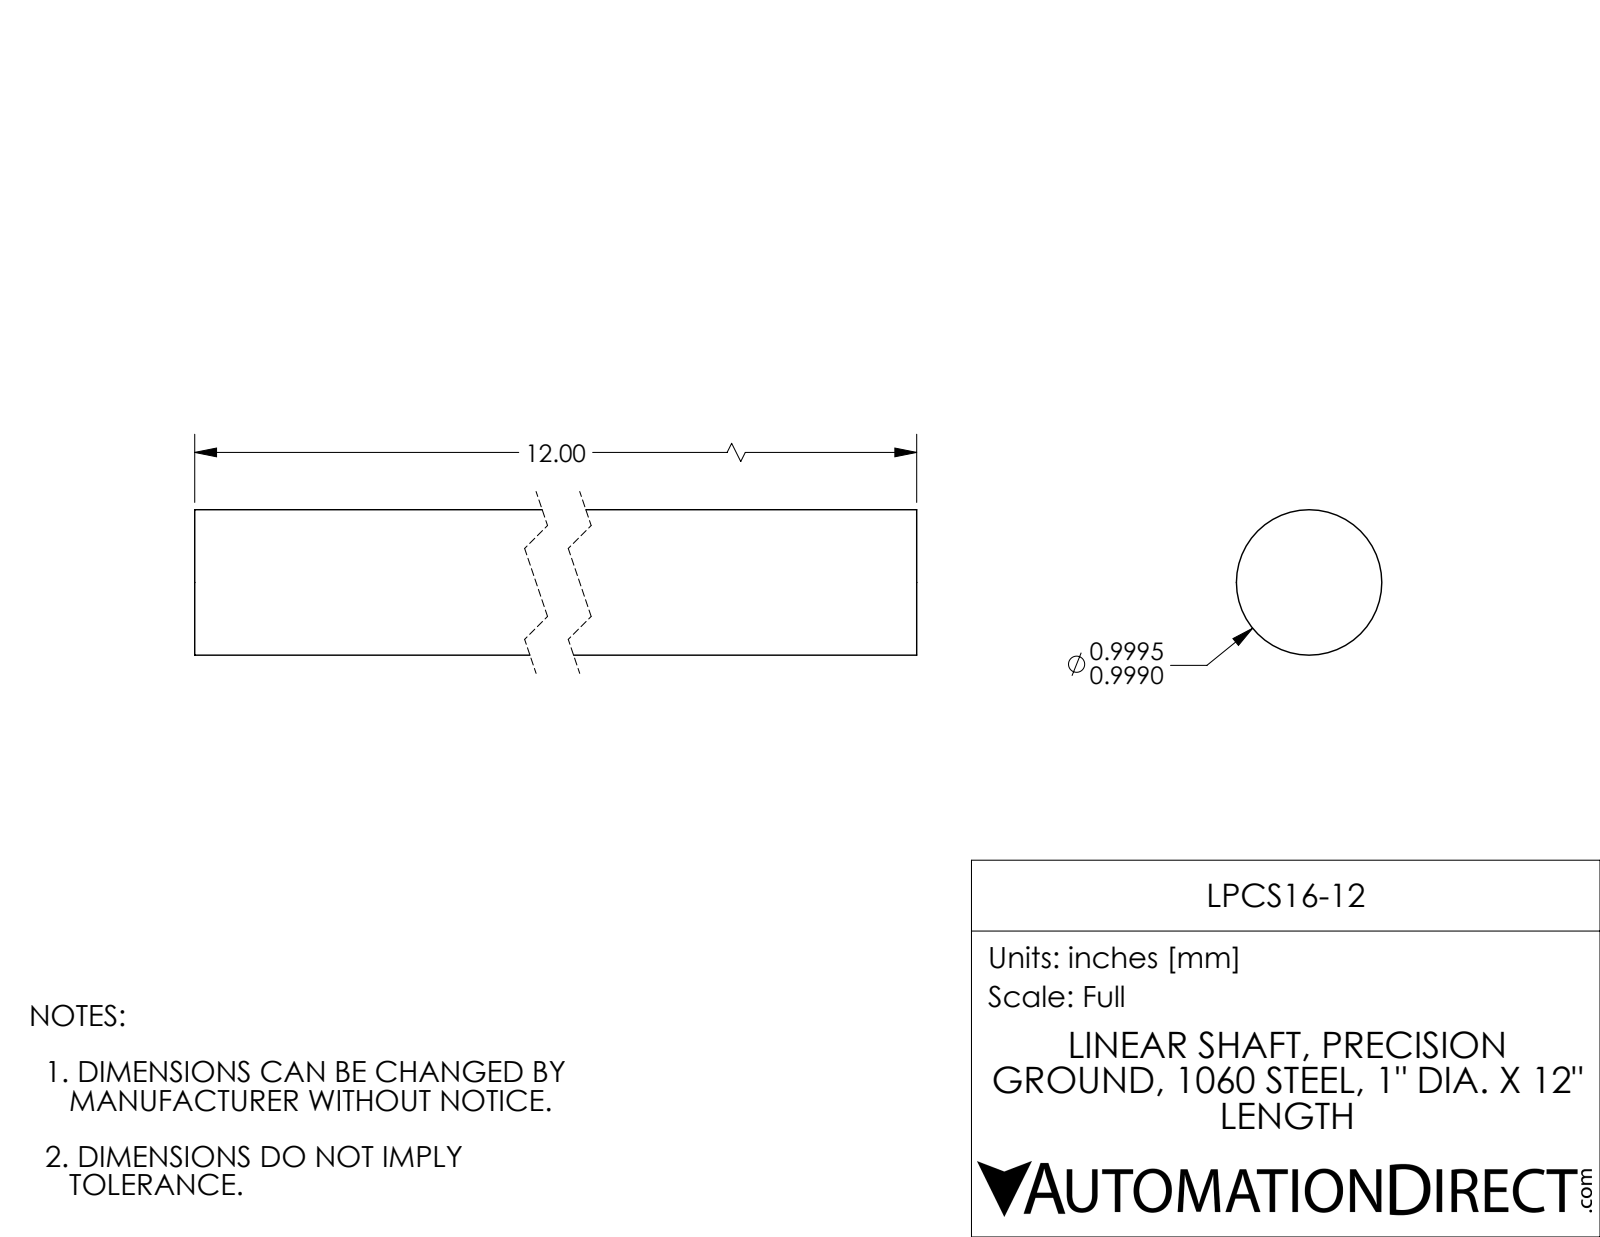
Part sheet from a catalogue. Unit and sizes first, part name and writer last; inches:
Units: inches
Overall size (bounding box): 12 × 0.999 × 0.999
Round bosses / shafts (diameter × count): ⌀1 ×1
Main face-to-face distances: 12
Volume: 9.415 in³ · Surface area: 39.25 in²
Bodies: 1 solid, 4 faces (2 planar, 2 cylindrical, 0 other)
Part name (STEP PRODUCT): LPCS16-12
STEP written by: SolidWorks 2017 (AUTOMOTIVE_DESIGN)
